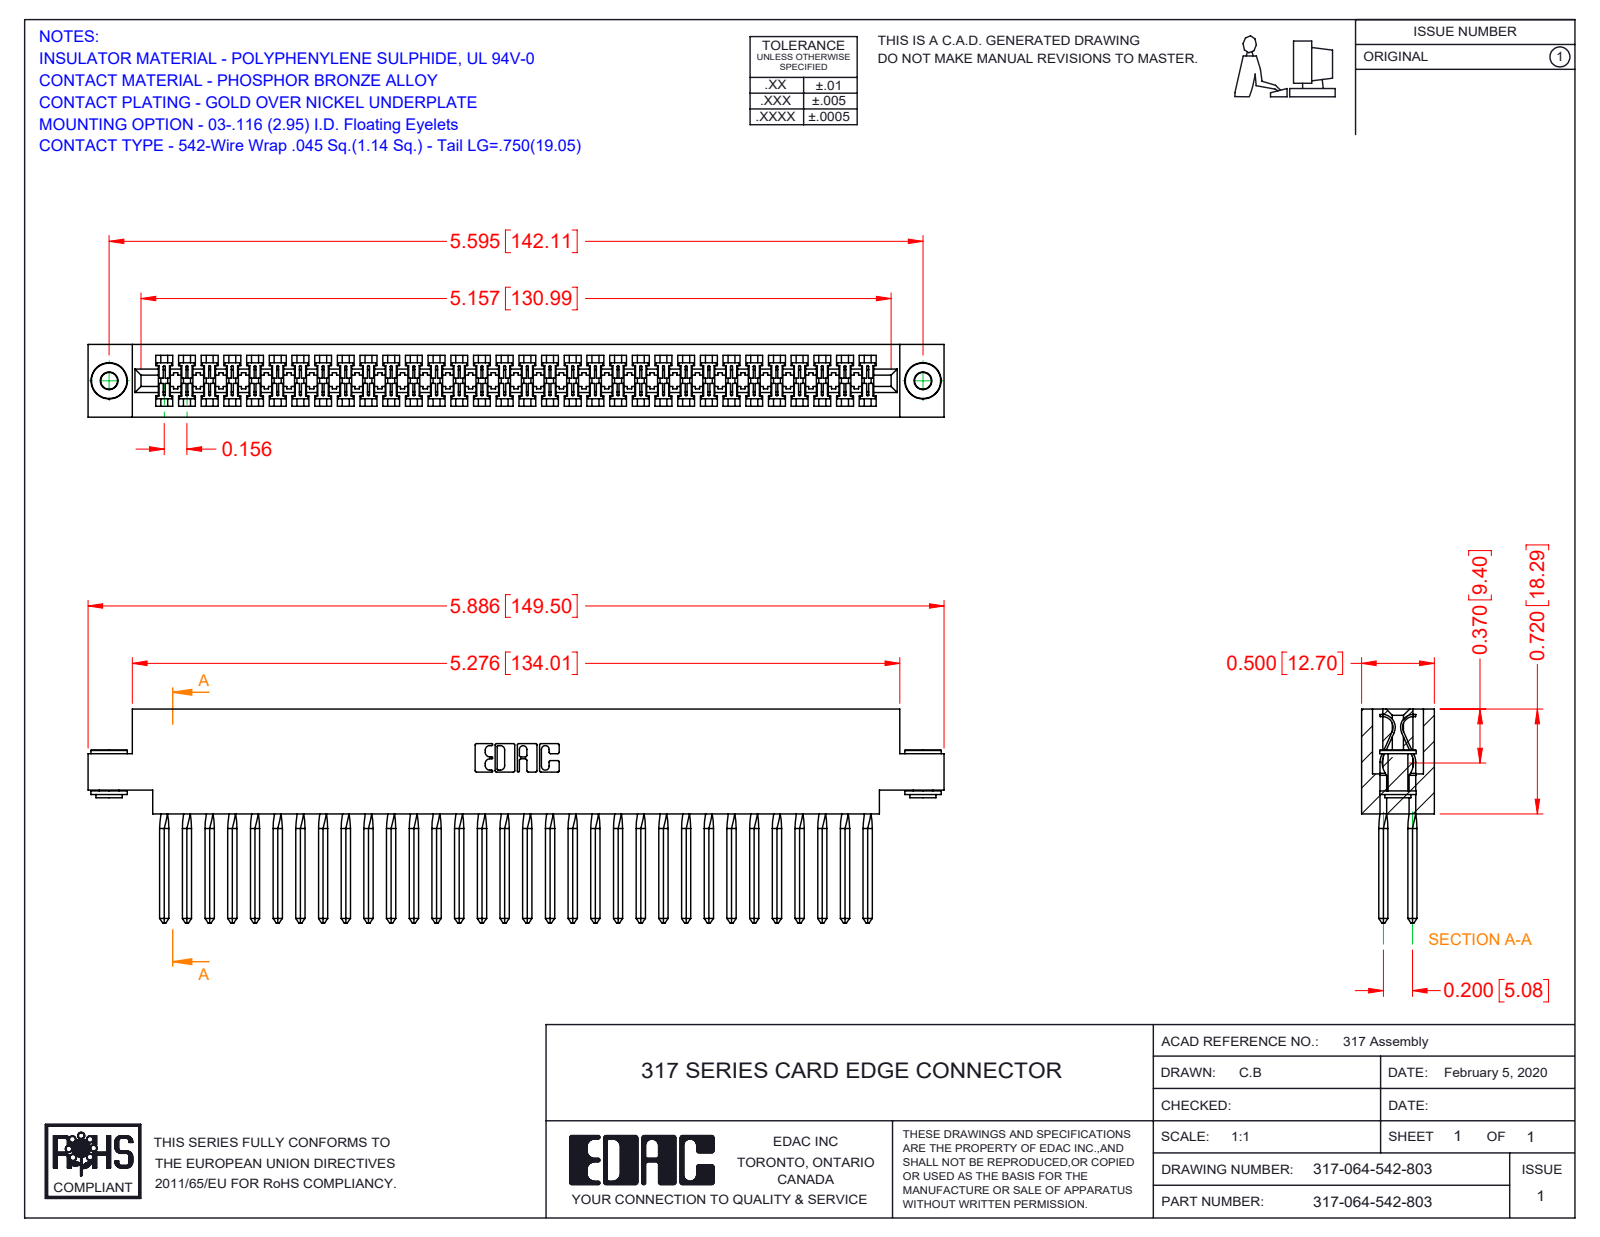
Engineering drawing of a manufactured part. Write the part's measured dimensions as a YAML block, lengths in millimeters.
part_name: "345-250-002_345-250-002-102; 317 Part_.156 Dia - TH; 317-064-542-803; 317-290-003_542"
step_written_by: "SolidWorks 2016 (CONFIG_CONTROL_DESIGN)"
units: millimeters
bodies: {solids: 67, faces: 3788, planar: 3012, cylindrical: 512, other: 264}
overall_size: [149.5, 37.3, 12.7]
volume: 24190
surface_area: 33530
round_holes:
  - {diameter: 2.9, count: 2}
  - {diameter: 4, count: 2}
round_bosses_or_shafts:
  - {diameter: 6.4, count: 2}
  - {diameter: 4.6, count: 2}
  - {diameter: 3.5, count: 2}
partial_cylinders:
  - {radius: 0.2, count: 128}
  - {radius: 0.3, count: 22}
  - {radius: 0.2, count: 6}
  - {radius: 0.8, count: 6}
  - {radius: 0.7, count: 3}
  - {radius: 1.9, count: 2}
  - {radius: 2.3, count: 2}
  - {radius: 2.5, count: 2}
face_to_face_distances: [12.7, 1.9, 10.8, 8.9, 5.1, 2.9, 2.8, 1.2, 3.3, 9.4]
hole_center_spacings: [142.1]
